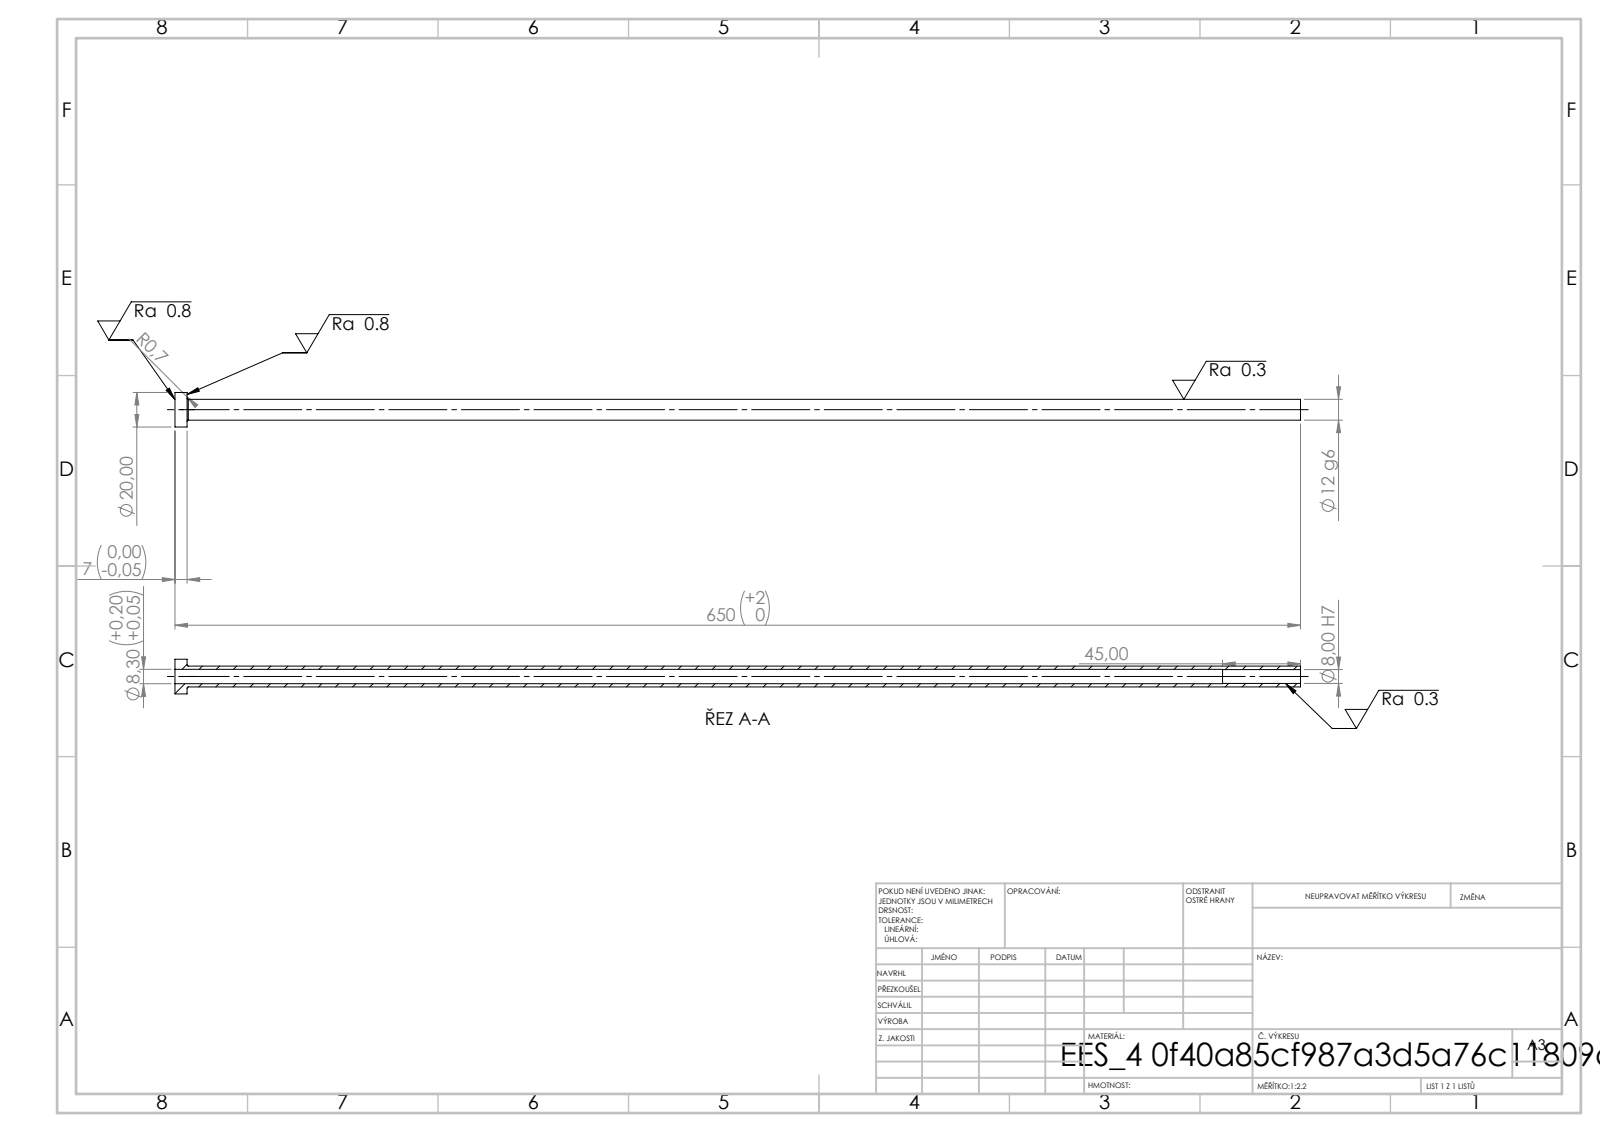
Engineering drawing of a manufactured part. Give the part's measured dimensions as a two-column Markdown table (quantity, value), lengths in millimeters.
| quantity | value |
| --- | --- |
| STEP written by | SolidWorks 2019 (CONFIG_CONTROL_DESIGN) |
| units | millimeters |
| bodies | 1 solid, 14 faces (4 planar, 8 cylindrical, 2 other) |
| overall size | 650 × 20 × 20 |
| volume | 39 929 mm³ |
| surface area | 42 104 mm² |
| round holes (diameter × count) | 8 × 1, 8.3 × 1 |
| round bosses / shafts (diameter × count) | 20 × 1, 12 × 1 |
| main face-to-face distances | 7, 650, 643, 605, 598, 45 |
